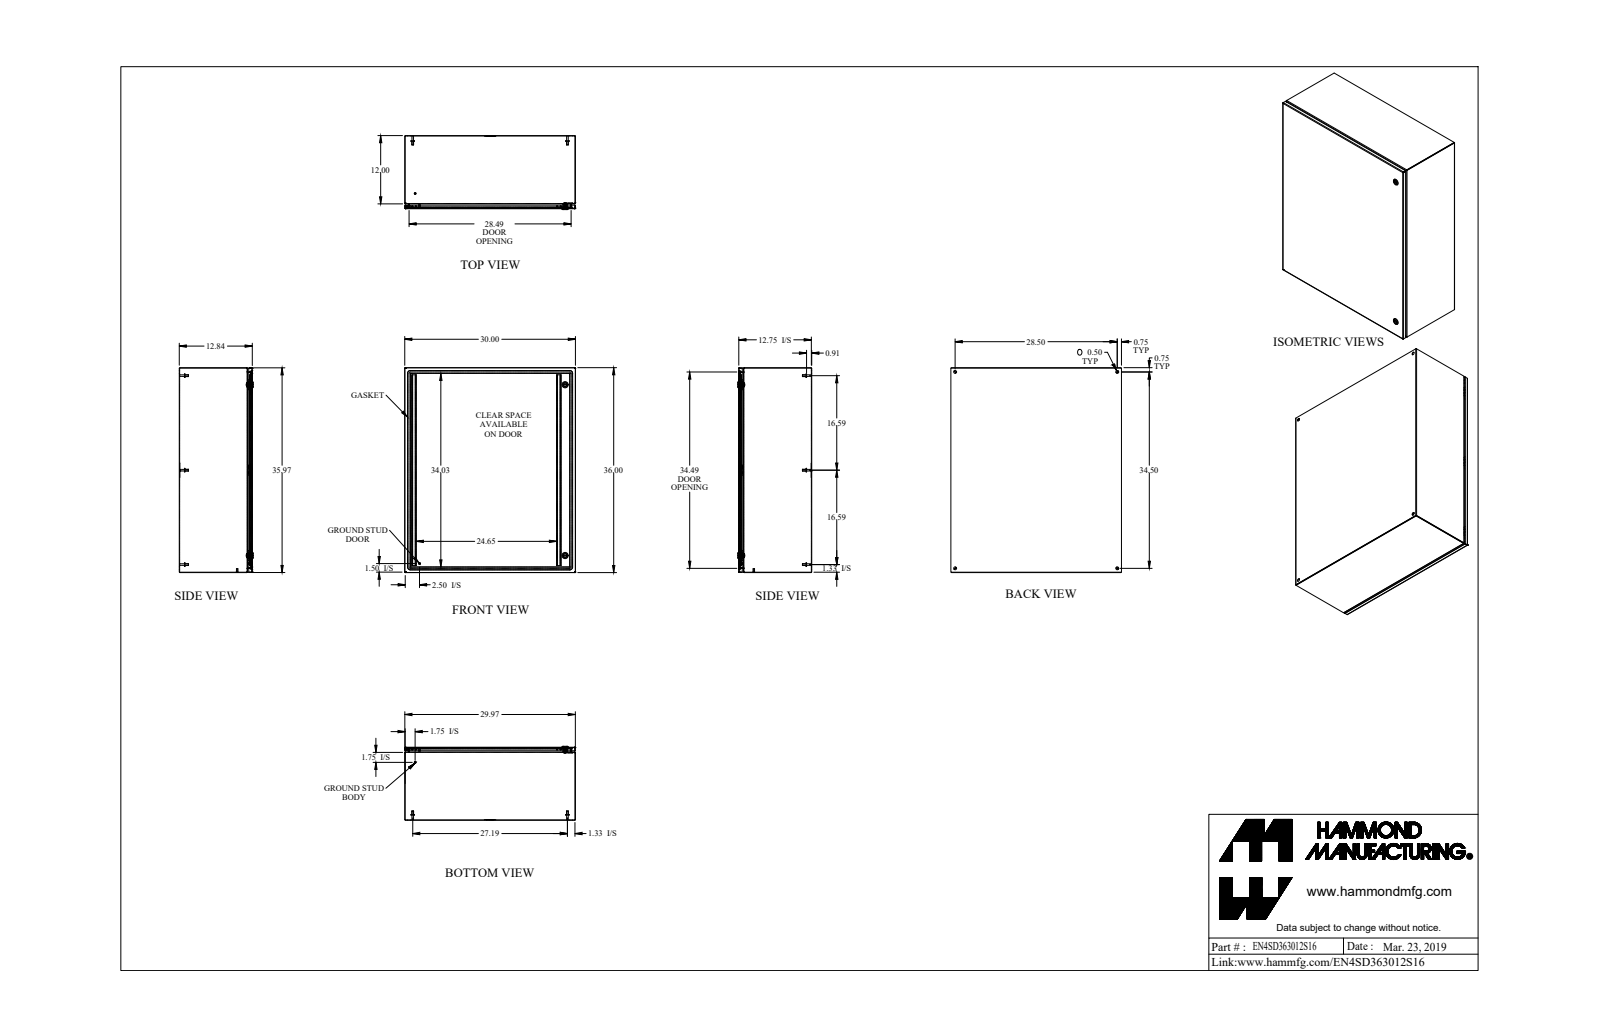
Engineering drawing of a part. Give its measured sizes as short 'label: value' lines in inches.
name: EN4SD363012S16
written by: SolidWorks 2019 (AUTOMOTIVE_DESIGN)
unit: in
bodies: 37 solids, 943 faces (454 planar, 309 cylindrical, 180 other)
size: 36 × 30 × 13.002
volume: 305.3 in³; area: 8 565 in²
holes: 6× ⌀0.5, 2× ⌀0.197, 2× ⌀0.387, 2× ⌀0.63, 2× ⌀0.768, 1× ⌀0.172, 1× ⌀0.24, 1× ⌀0.242
bosses: 8× ⌀0.625, 8× ⌀0.313, 6× ⌀0.275, 2× ⌀1.1, 2× ⌀0.785, 2× ⌀0.525, 2× ⌀0.25, 2× ⌀0.236
rounds: 18× R0.036, 18× R0.108, 12× R0.01, 12× R0.048, 12× R0.312, 6× R0.006, 6× R0.062, 4× R0.125
face distances: 0.072, 12.77, 12.698, 12.842, 29.928, 35.928, 29.856, 30, 35.856, 36
hole spacings: 27.531, 28.5, 34.5, 44.749, 2.488, 2.489, 29.999, 32.266
